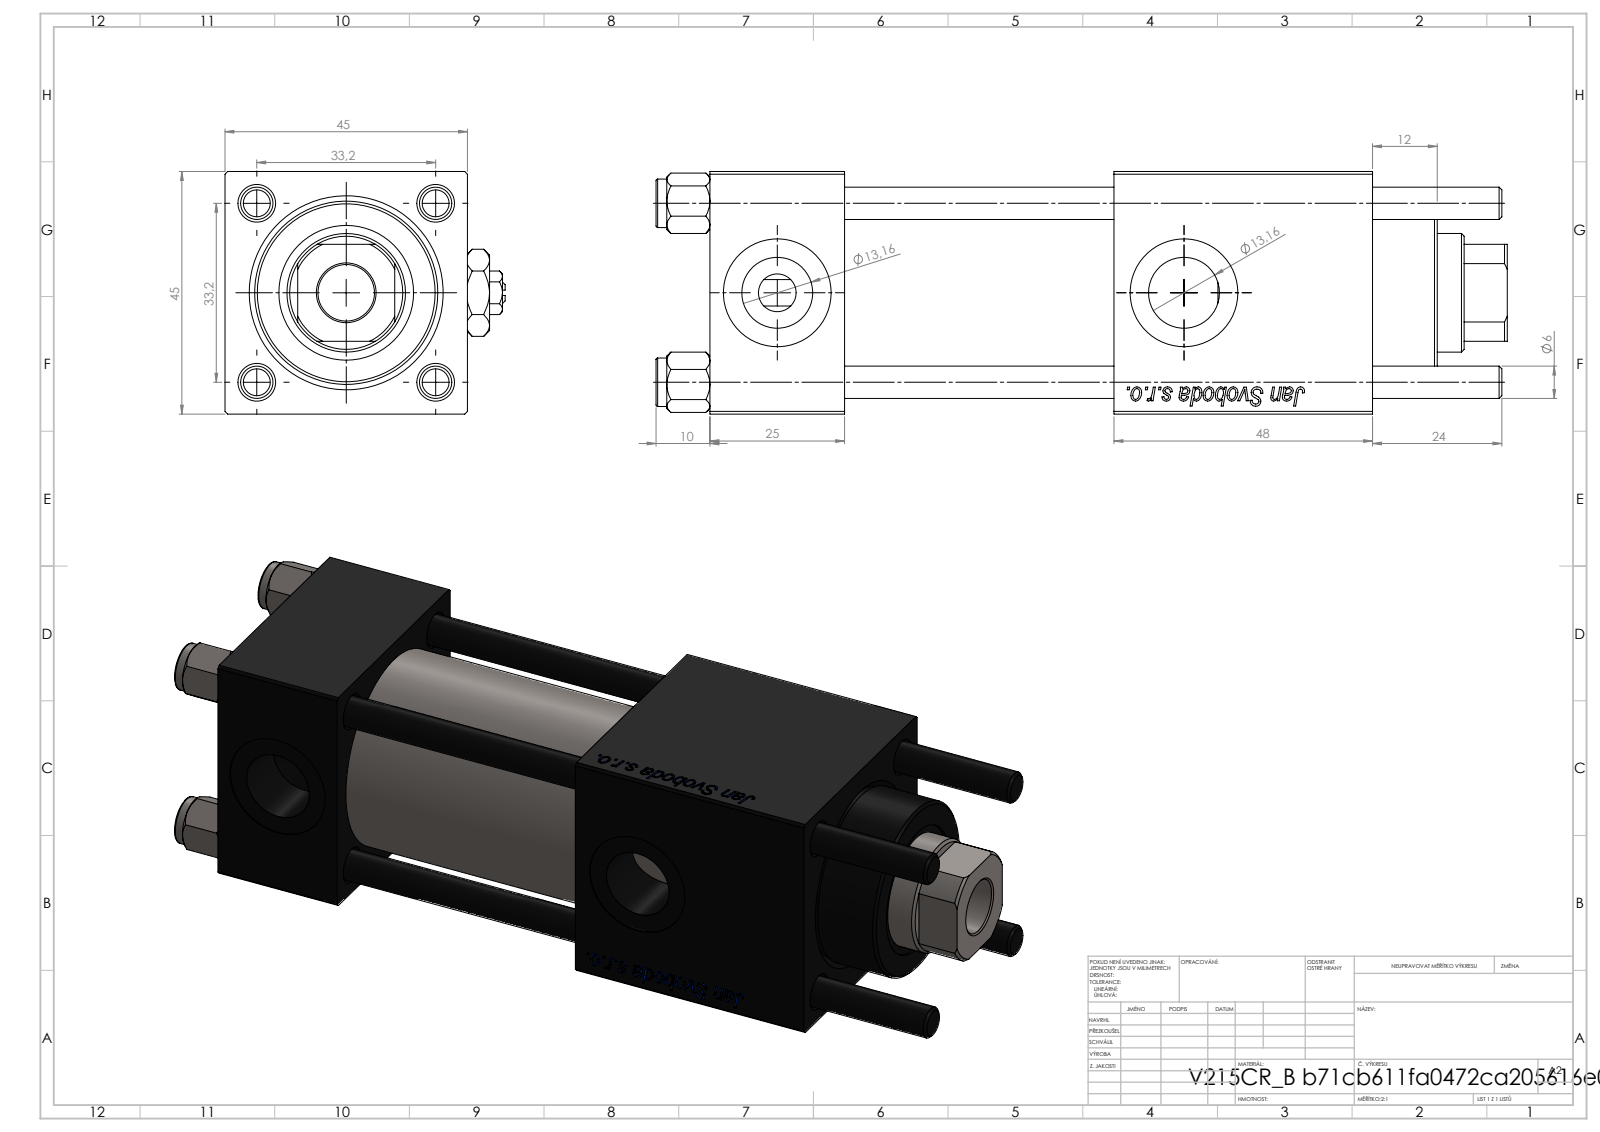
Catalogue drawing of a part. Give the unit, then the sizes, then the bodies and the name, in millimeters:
Units: millimetres
Overall size (bounding box): 158 × 52 × 45
Round holes (diameter × count): ⌀6 ×4, ⌀7 ×2, ⌀13.16 ×2, ⌀20 ×2, ⌀10.5 ×1, ⌀22 ×1, ⌀24 ×1, ⌀25 ×1, ⌀32 ×1, ⌀33 ×1
Round bosses / shafts (diameter × count): ⌀9 ×4, ⌀38 ×1, ⌀34 ×1
Partial cylindrical surfaces — rounded edges, fillets, slot ends (radius × count): R10.5 ×1
Main face-to-face distances: 45, 25, 50, 123, 75, 98, 48, 94.3, 69.3, 19.3
Hole centre spacings: 23.48, 33.2, 46.95, 75.5
Volume: 213 630 mm³ · Surface area: 77 550 mm²
Bodies: 12 solids, 1205 faces (455 planar, 82 cylindrical, 668 other)
Part name (STEP PRODUCT): Zatka_pro_OIL_PORT; V215CR_B-1; V215CR_VCP_B; V215CR_B_TYCINKA (+2 more)
STEP written by: SolidWorks 2019 (CONFIG_CONTROL_DESIGN)
